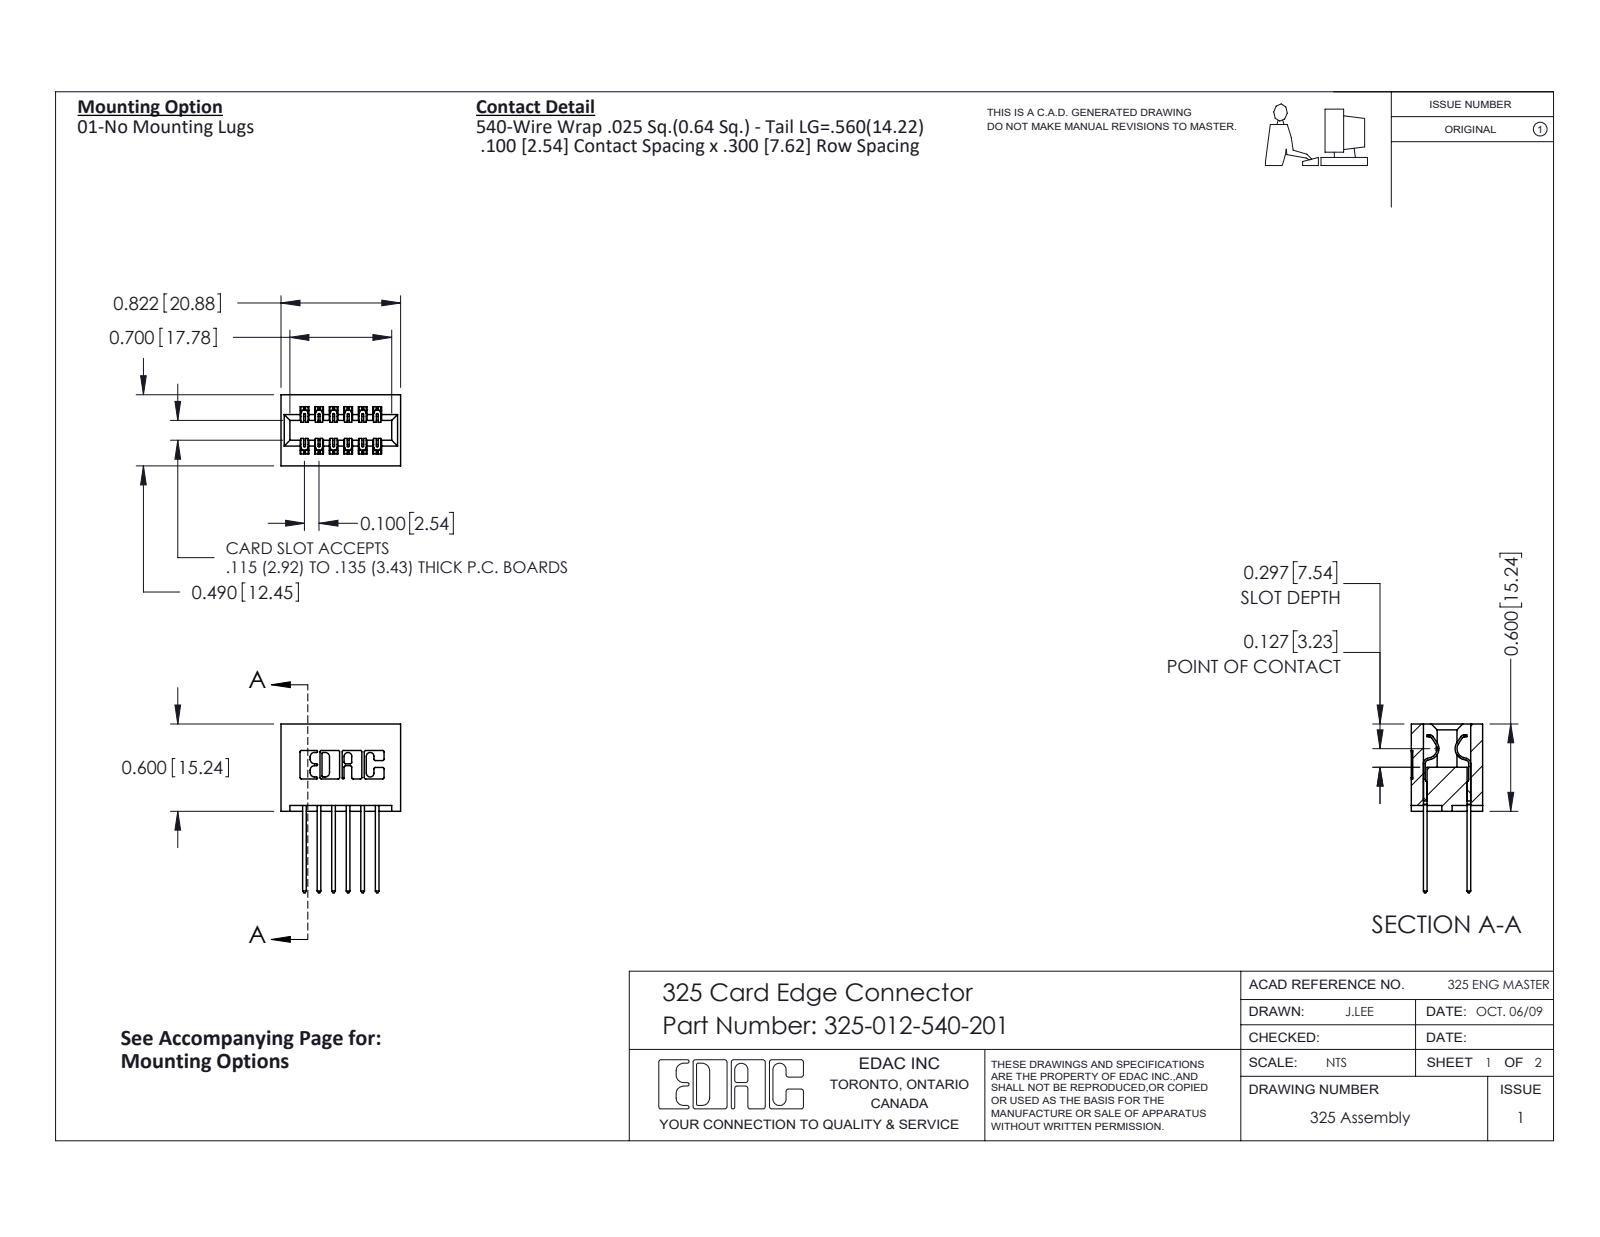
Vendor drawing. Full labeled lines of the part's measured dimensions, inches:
Part name (STEP PRODUCT): 325-292-001_325-293-140; 325 Part_Lugless; 325-012-540-201
STEP written by: SolidWorks 2016 (CONFIG_CONTROL_DESIGN)
Units: inches
Bodies: 13 solids, 730 faces (498 planar, 232 cylindrical, 0 other)
Overall size (bounding box): 1.16 × 0.822 × 0.49
Volume: 0.185 in³ · Surface area: 5.71 in²
Partial cylindrical surfaces — rounded edges, fillets, slot ends (radius × count): R0.01 ×22, R0.006 ×18, R0.01 ×12, R0.007 ×6, R0.031 ×6, R0.026 ×3, R0.014 ×2, R0.022 ×2
Main face-to-face distances: 0.3, 0.083, 0.407, 0.1, 0.2, 0.383, 0.107, 0.025, 0.04, 0.06
